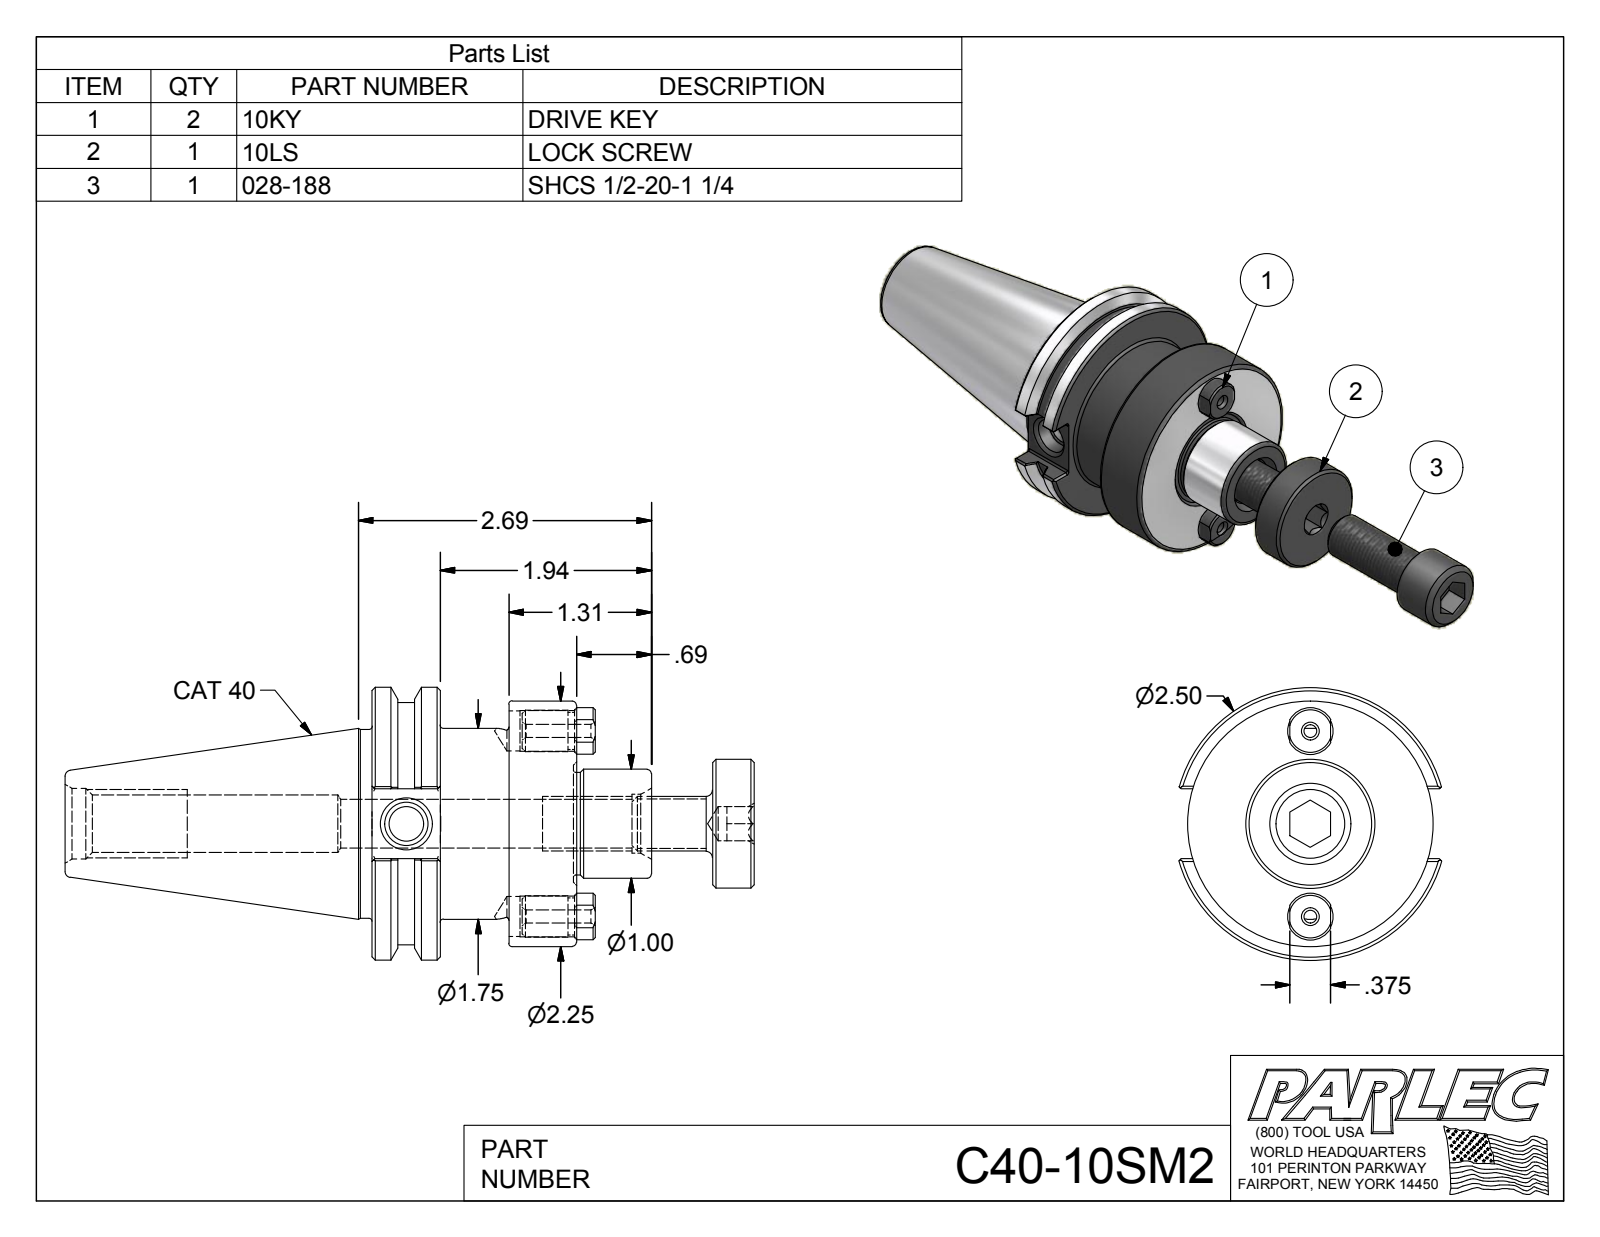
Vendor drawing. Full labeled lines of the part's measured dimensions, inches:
Part name (STEP PRODUCT): C40-10SM2; C40-10SM2-1; 10KY; 028-188 (+1 more)
STEP written by: Autodesk Inventor 2012 (AUTOMOTIVE_DESIGN)
Units: inches
Bodies: 5 solids, 178 faces (69 planar, 48 cylindrical, 61 other)
Overall size (bounding box): 8.44 × 2.5 × 2.406
Volume: 11.31 in³ · Surface area: 59.73 in²
Round holes (diameter × count): ⌀0.12 ×2, ⌀0.368 ×2, ⌀0.374 ×2, ⌀0.312 ×1, ⌀0.315 ×1, ⌀0.399 ×1, ⌀0.446 ×1, ⌀0.527 ×1, ⌀0.54 ×1, ⌀0.648 ×1
Round bosses / shafts (diameter × count): ⌀0.38 ×2, ⌀0.34 ×2, ⌀2.5 ×1, ⌀2.25 ×1, ⌀2.219 ×1, ⌀1.75 ×1, ⌀1.73 ×1, ⌀1.18 ×1
Partial cylindrical surfaces — rounded edges, fillets, slot ends (radius × count): R0.02 ×12, R0.214 ×2
Main face-to-face distances: 1.25, 1.875, 0.625, 1.255, 0.63, 0.62, 3.502, 2.877, 2.247, 1.627
Hole centre spacings: 0.85, 1.7
